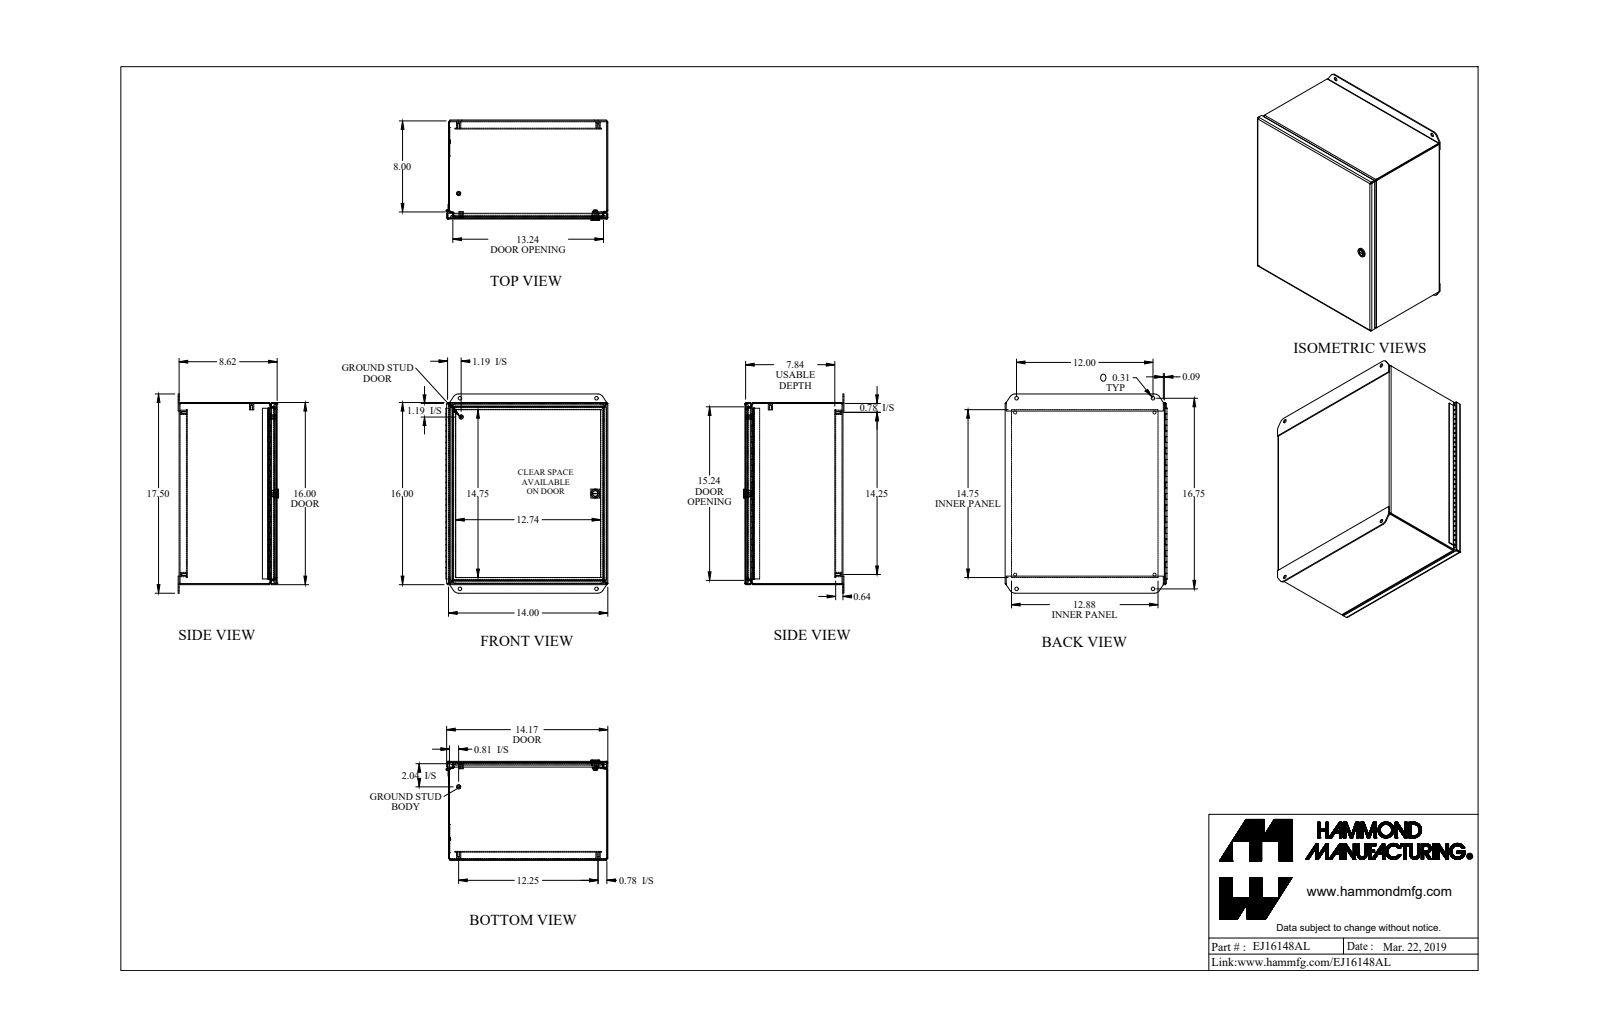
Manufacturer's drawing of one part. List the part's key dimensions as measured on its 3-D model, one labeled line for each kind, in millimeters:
Part name (STEP PRODUCT): EJ16148AL_Default
STEP written by: SolidWorks 2019 (CONFIG_CONTROL_DESIGN)
Units: millimetres
Bodies: 14 solids, 730 faces (500 planar, 162 cylindrical, 68 other)
Overall size (bounding box): 444.5 × 361.3 × 224
Volume: 1 693 000 mm³ · Surface area: 1 695 000 mm²
Round holes (diameter × count): ⌀4 ×6, ⌀6.7 ×4, ⌀8 ×4, ⌀13.1 ×1
Round bosses / shafts (diameter × count): ⌀9.5 ×6, ⌀8.4 ×6, ⌀20 ×1, ⌀13.6 ×1, ⌀12.6 ×1, ⌀11 ×1, ⌀4.6 ×1, ⌀2.5 ×1
Partial cylindrical surfaces — rounded edges, fillets, slot ends (radius × count): R1 ×16, R3.1 ×16, R7.1 ×12, R6.4 ×4, R12.7 ×4, R12.7 ×4, R1.5 ×2, R0.8 ×1
Main face-to-face distances: 2.1, 216.8, 218.9, 353.5, 404.3, 214.8, 16.3, 14.3, 202.5, 200.5
Hole centre spacings: 31.9, 309.6, 393.7, 499.8, 0.6, 181.1, 212.8, 304.8
